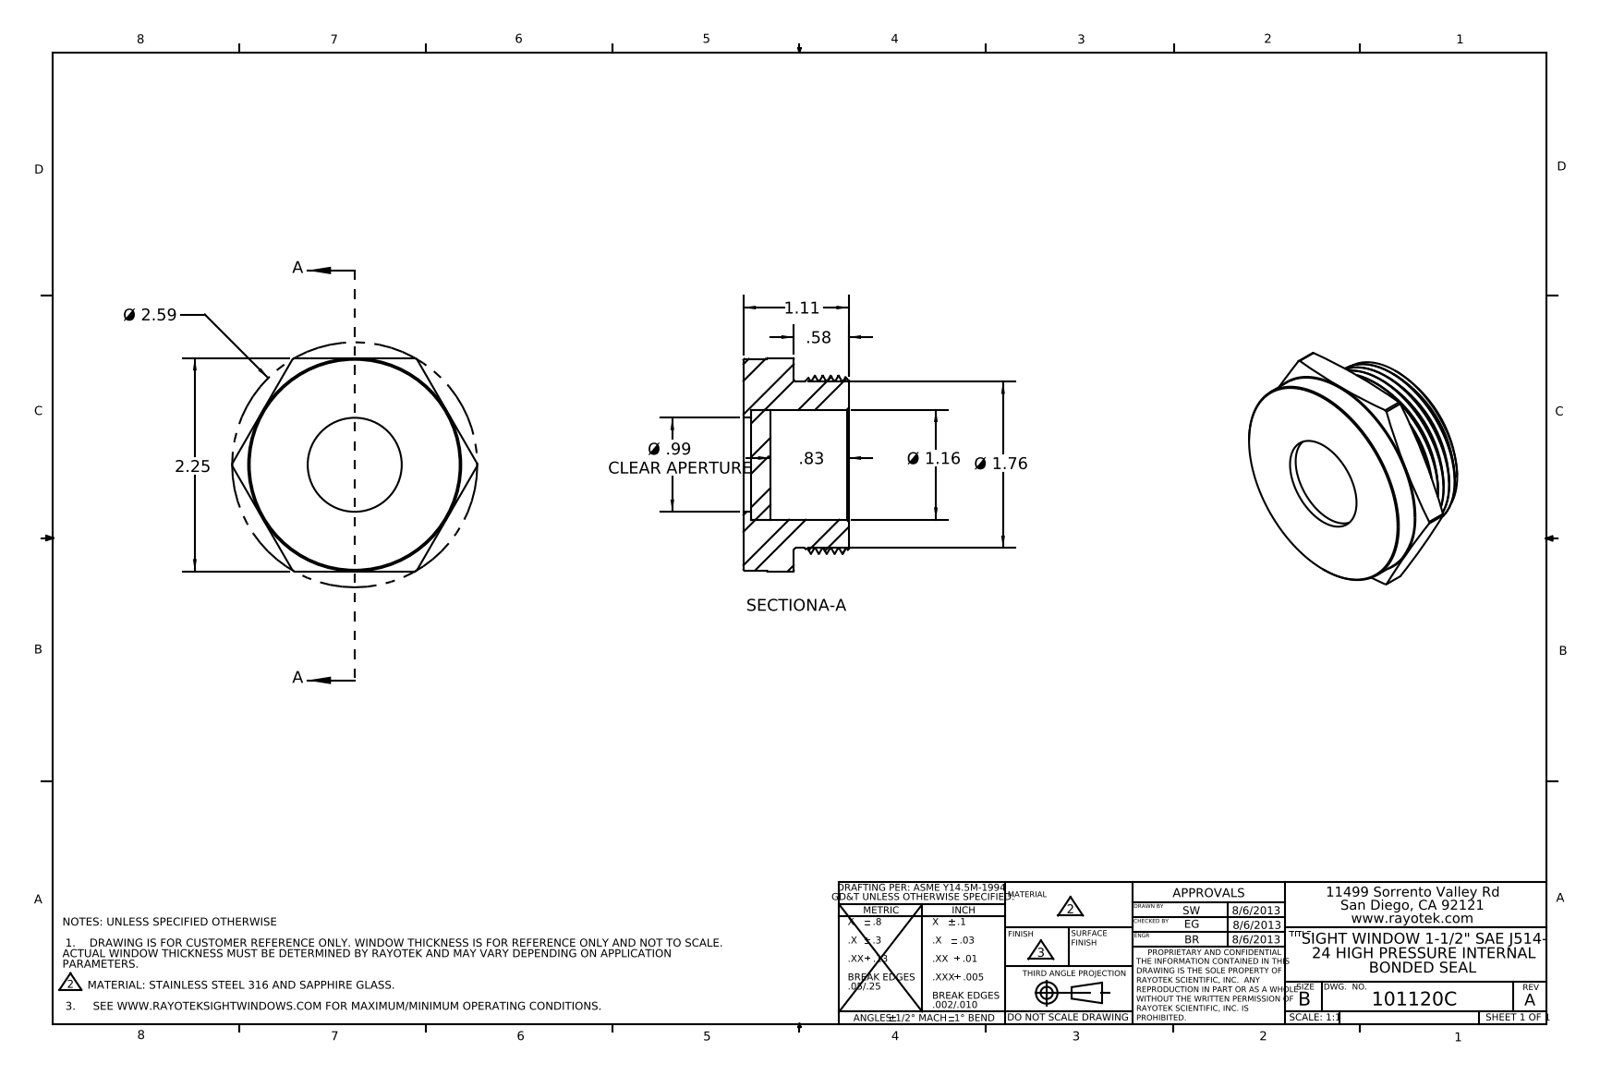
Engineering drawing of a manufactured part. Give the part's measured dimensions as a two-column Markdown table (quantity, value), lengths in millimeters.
| quantity | value |
| --- | --- |
| part name | 403120 |
| STEP written by | SolidWorks 2012 (AUTOMOTIVE_DESIGN) |
| units | millimeters |
| bodies | 2 solids, 61 faces (12 planar, 26 cylindrical, 23 other) |
| overall size | 65.7 × 57.2 × 28.2 |
| volume | 44 850 mm³ |
| surface area | 14 630 mm² |
| round holes (diameter × count) | 25.2 × 1, 29.5 × 1 |
| round bosses / shafts (diameter × count) | 56.8 × 1, 47.6 × 1, 44.6 × 1 |
| partial cylindrical surfaces (radius × count) | 32.8 × 1 |
| main face-to-face distances | 13.5, 14.7, 28.2, 26.1, 11.3, 2.1, 21, 6.2, 5.1, 7.2 |
